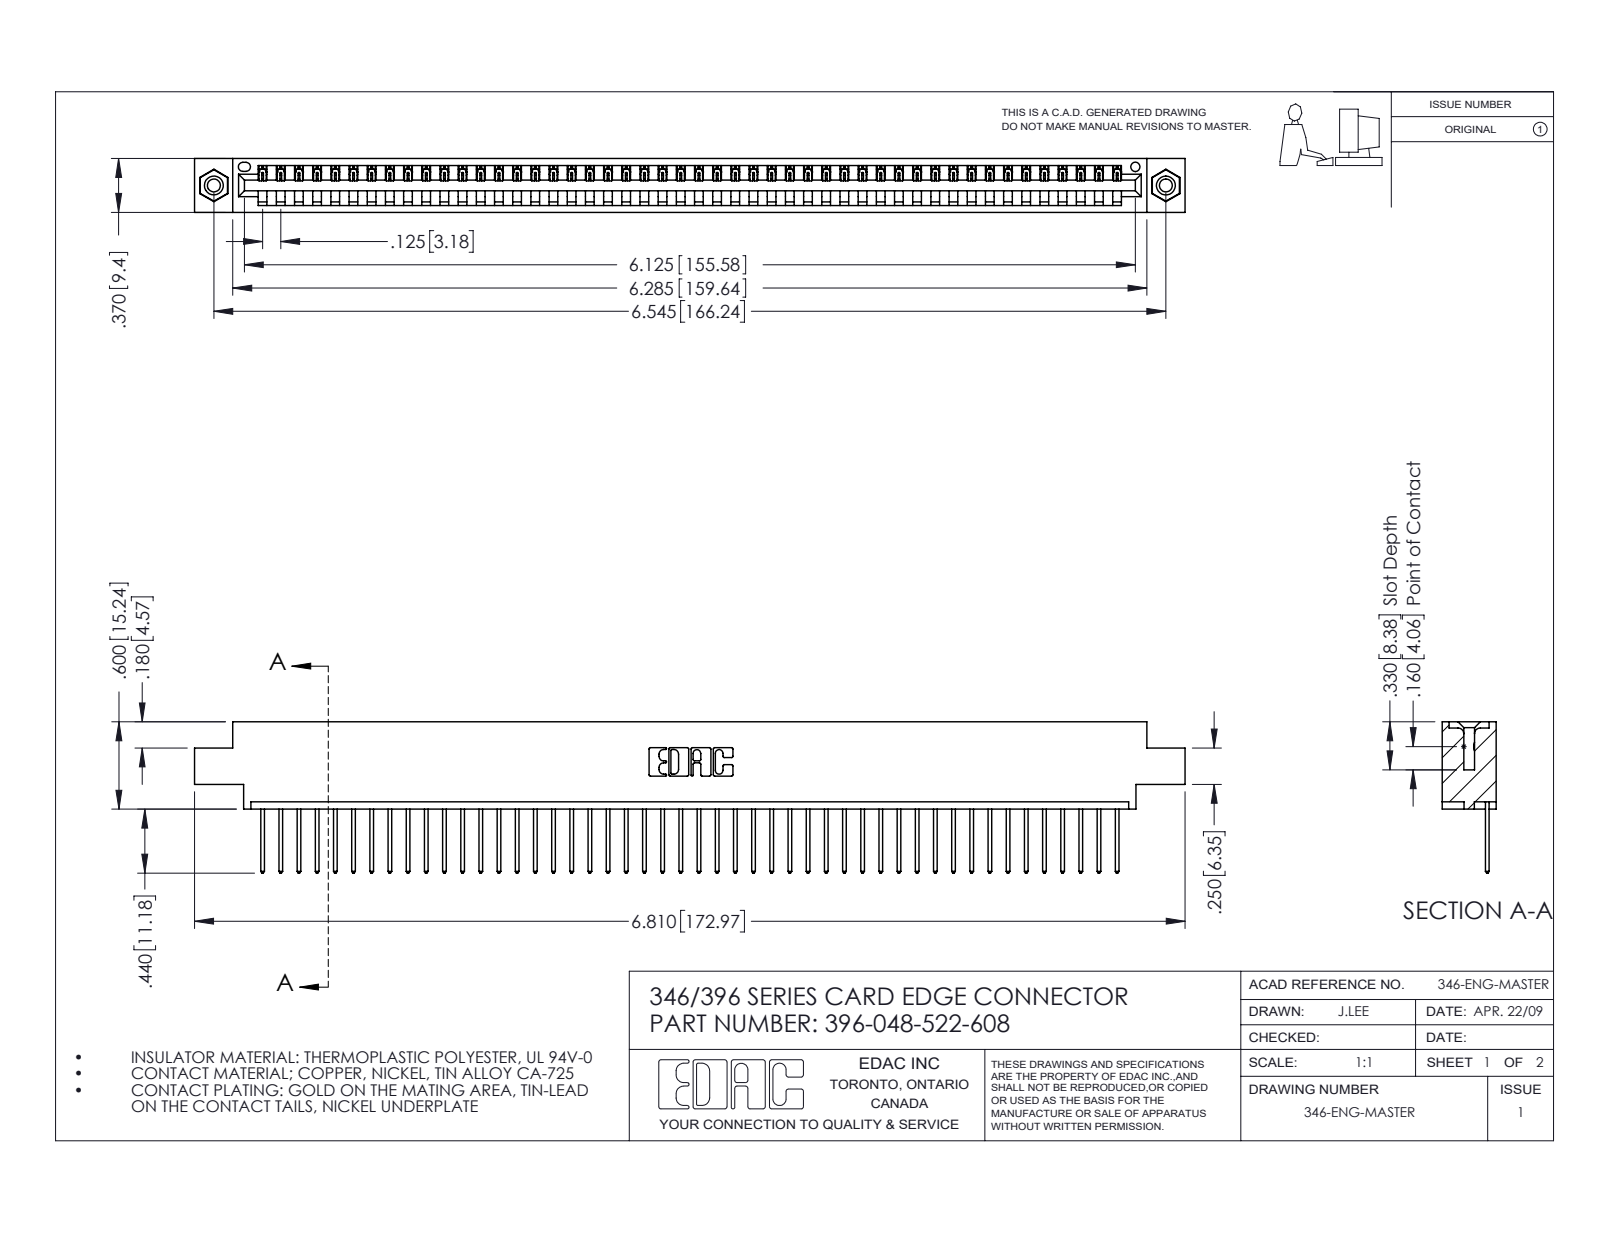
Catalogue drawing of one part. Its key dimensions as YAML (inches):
part_name: "396-048-522-608; 346 Part_0.170 Offset - 0.156 Dia-TI; 345-292-001_345-293-122; 345-250-001_345-250-003-102"
step_written_by: "SolidWorks 2016 (CONFIG_CONTROL_DESIGN)"
units: inches
bodies: {solids: 51, faces: 2970, planar: 2032, cylindrical: 922, other: 16}
overall_size: [6.81, 1.04, 0.37]
volume: 1.003
surface_area: 32.51
round_holes:
  - {diameter: 0.089, count: 2}
  - {diameter: 0.125, count: 2}
  - {diameter: 0.156, count: 2}
  - {diameter: 0.064, count: 1}
round_bosses_or_shafts:
  - {diameter: 0.155, count: 2}
partial_cylinders:
  - {radius: 0.006, count: 96}
  - {radius: 0.01, count: 96}
  - {radius: 0.01, count: 22}
  - {radius: 0.007, count: 6}
  - {radius: 0.031, count: 6}
  - {radius: 0.026, count: 3}
  - {radius: 0.031, count: 2}
  - {radius: 0.04, count: 2}
face_to_face_distances: [0.048, 0.322, 0.37, 0.25, 0.072, 0.298, 0.025, 0.222, 0.148, 0.1]
hole_center_spacings: [0.246, 6.336, 6.545]
